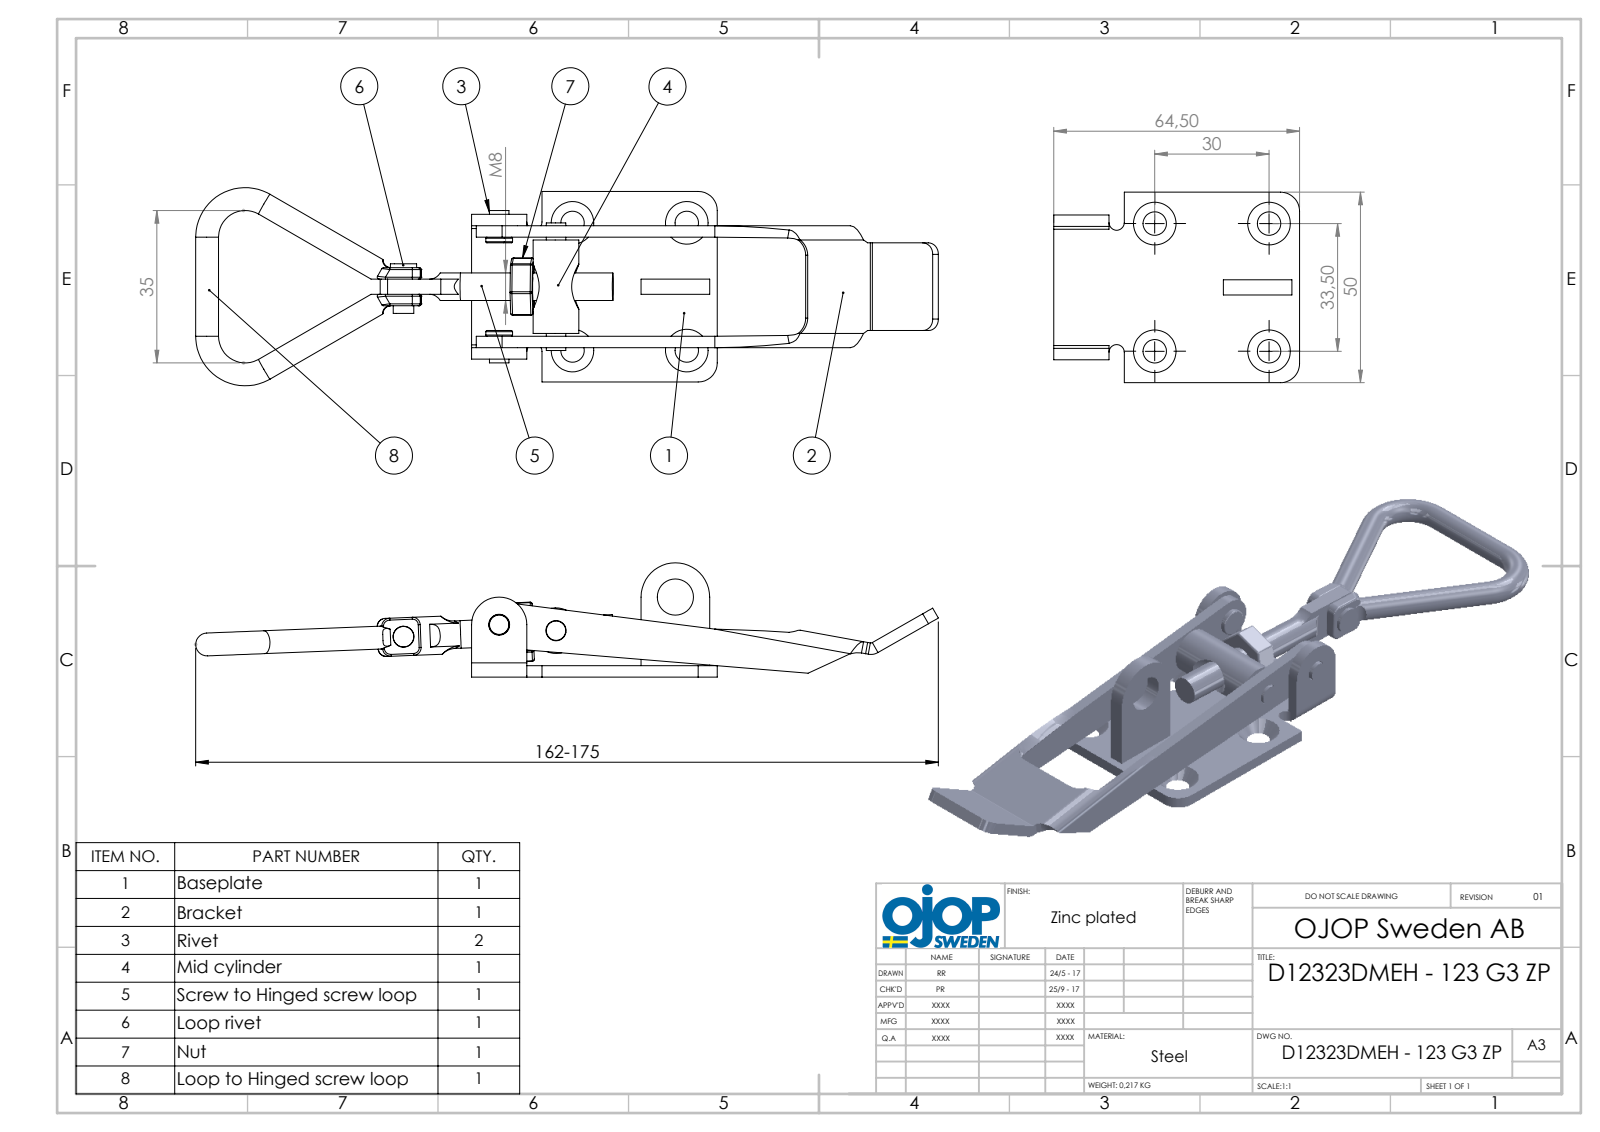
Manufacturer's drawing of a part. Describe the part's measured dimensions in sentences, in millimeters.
The part is named "skruvm8; rulle; ring m8; platta (+5 more)". Its 3-D file was written by "SolidWorks 2015 (AUTOMOTIVE_DESIGN)". It is 9 solids with 289 faces: 98 planar, 127 cylindrical and 64 other. Overall it measures 194.95 by 52 by 30 millimeters. Its volume is 29 857 cubic millimeters and its surface area 23 400 square millimeters. Round holes: 2 of diameter 5.3, 2 of diameter 5.5, 1 of diameter 6.8, 1 of diameter 7, 1 of diameter 9.5. Round bosses or shafts: 3 of diameter 6, 2 of diameter 5.1, 1 of diameter 12, 1 of diameter 7.25, 1 of diameter 7.2, 1 of diameter 7, 1 of diameter 6.9, 1 of diameter 5.4. Partial cylindrical surfaces (rounded edges, fillets, slot ends): 34 of radius 0.5, 12 of radius 2, 5 of radius 0.74, 5 of radius 3.74, 4 of radius 3, 4 of radius 5, 1 of radius 6, 1 of radius 7.25. The main face-to-face distances are 3, 29, 32, 18, 11, 14, 15, 26, 4, 6. The hole center spacings are 15.01, 25.31, 32.54, 40.07, 46.81, 72.11.
